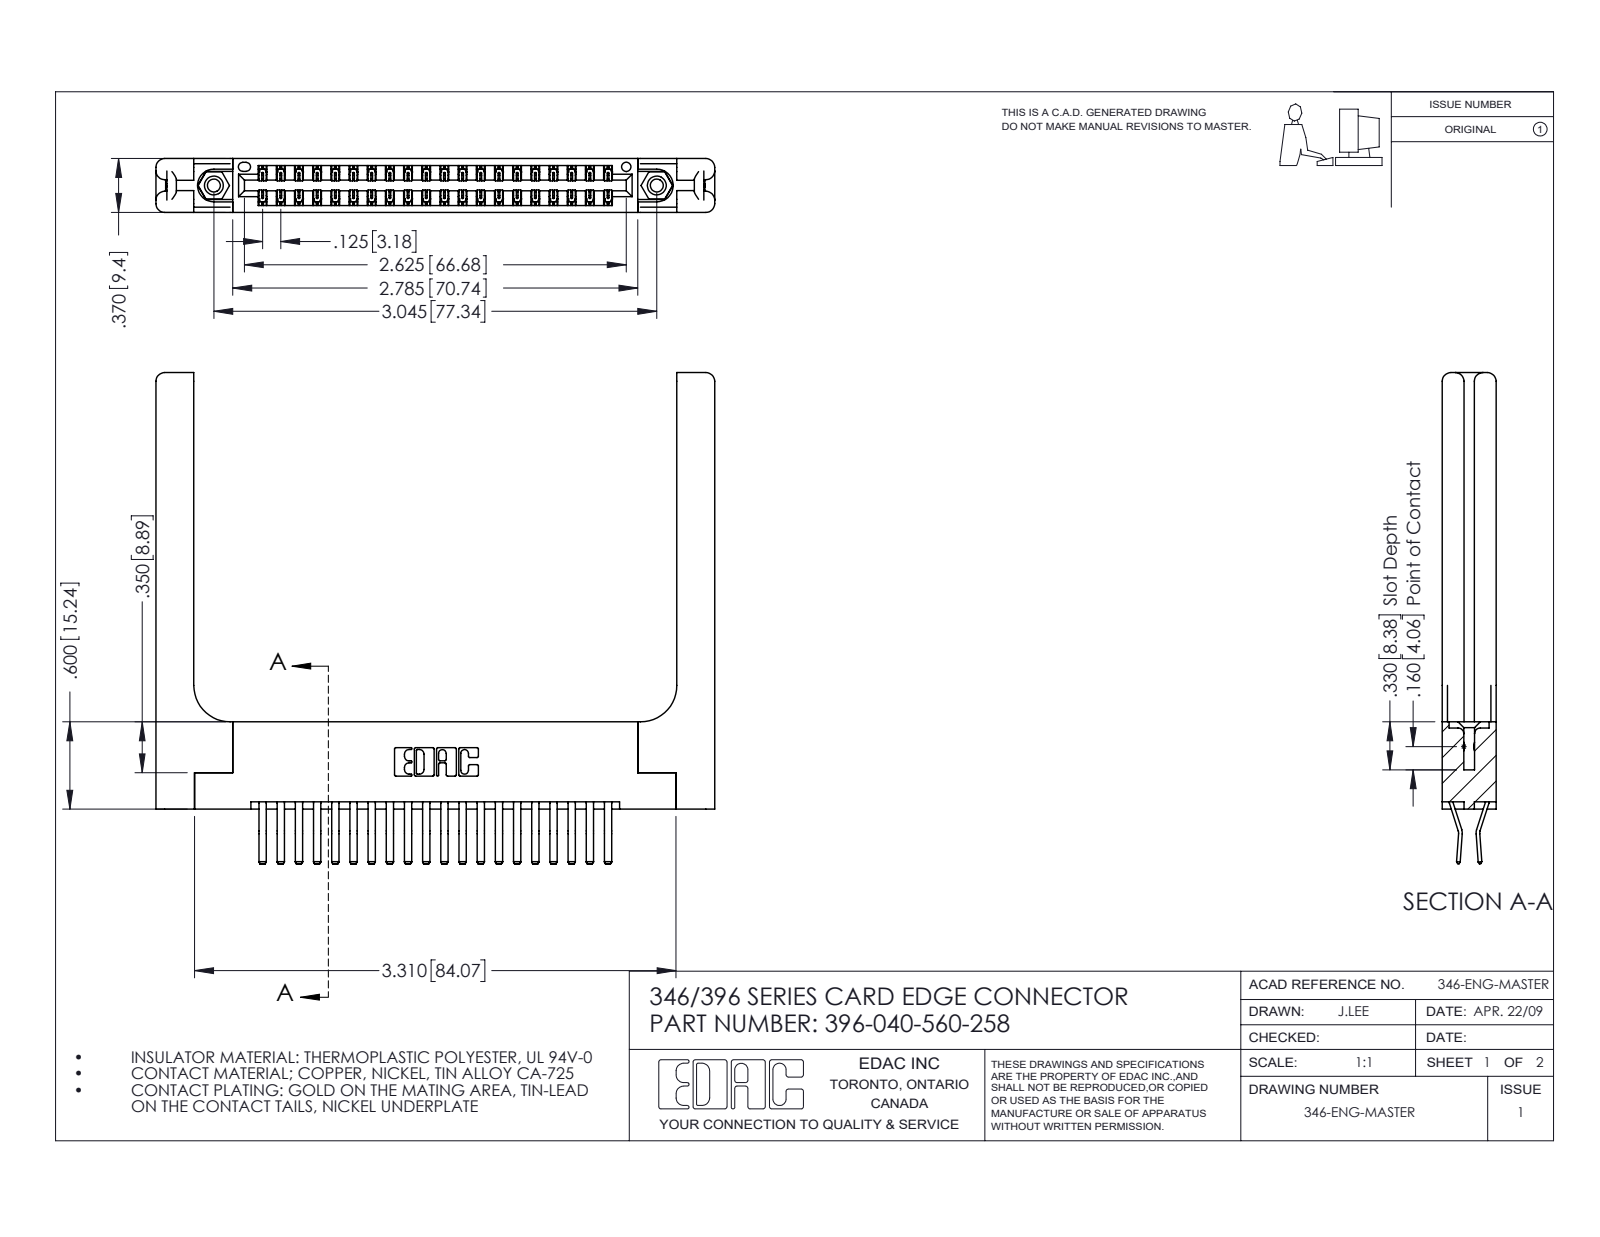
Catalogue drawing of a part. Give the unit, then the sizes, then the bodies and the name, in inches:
Units: inches
Overall size (bounding box): 3.841 × 3.375 × 0.37
Round holes (diameter × count): ⌀0.089 ×2, ⌀0.125 ×2, ⌀0.156 ×2, ⌀0.064 ×1
Round bosses / shafts (diameter × count): ⌀0.155 ×2
Partial cylindrical surfaces — rounded edges, fillets, slot ends (radius × count): R0.006 ×60, R0.01 ×22, R0.06 ×16, R0.007 ×6, R0.031 ×6, R0.026 ×3, R0.01 ×2, R0.014 ×2
Main face-to-face distances: 0.37, 0.072, 0.15, 0.148, 0.048, 0.322, 0.025, 0.25, 0.077, 0.102
Hole centre spacings: 0.246, 2.837, 3.045
Volume: 1.043 in³ · Surface area: 28.72 in²
Bodies: 45 solids, 2538 faces (1624 planar, 854 cylindrical, 60 other)
Part name (STEP PRODUCT): 346-220-058_345-220-058; 346 Part_Flush Mounting Lugs - 0.156 Dia-TH; 345-250-001_345-250-001-102; 396-040-560-258 (+1 more)
STEP written by: SolidWorks 2016 (CONFIG_CONTROL_DESIGN)
